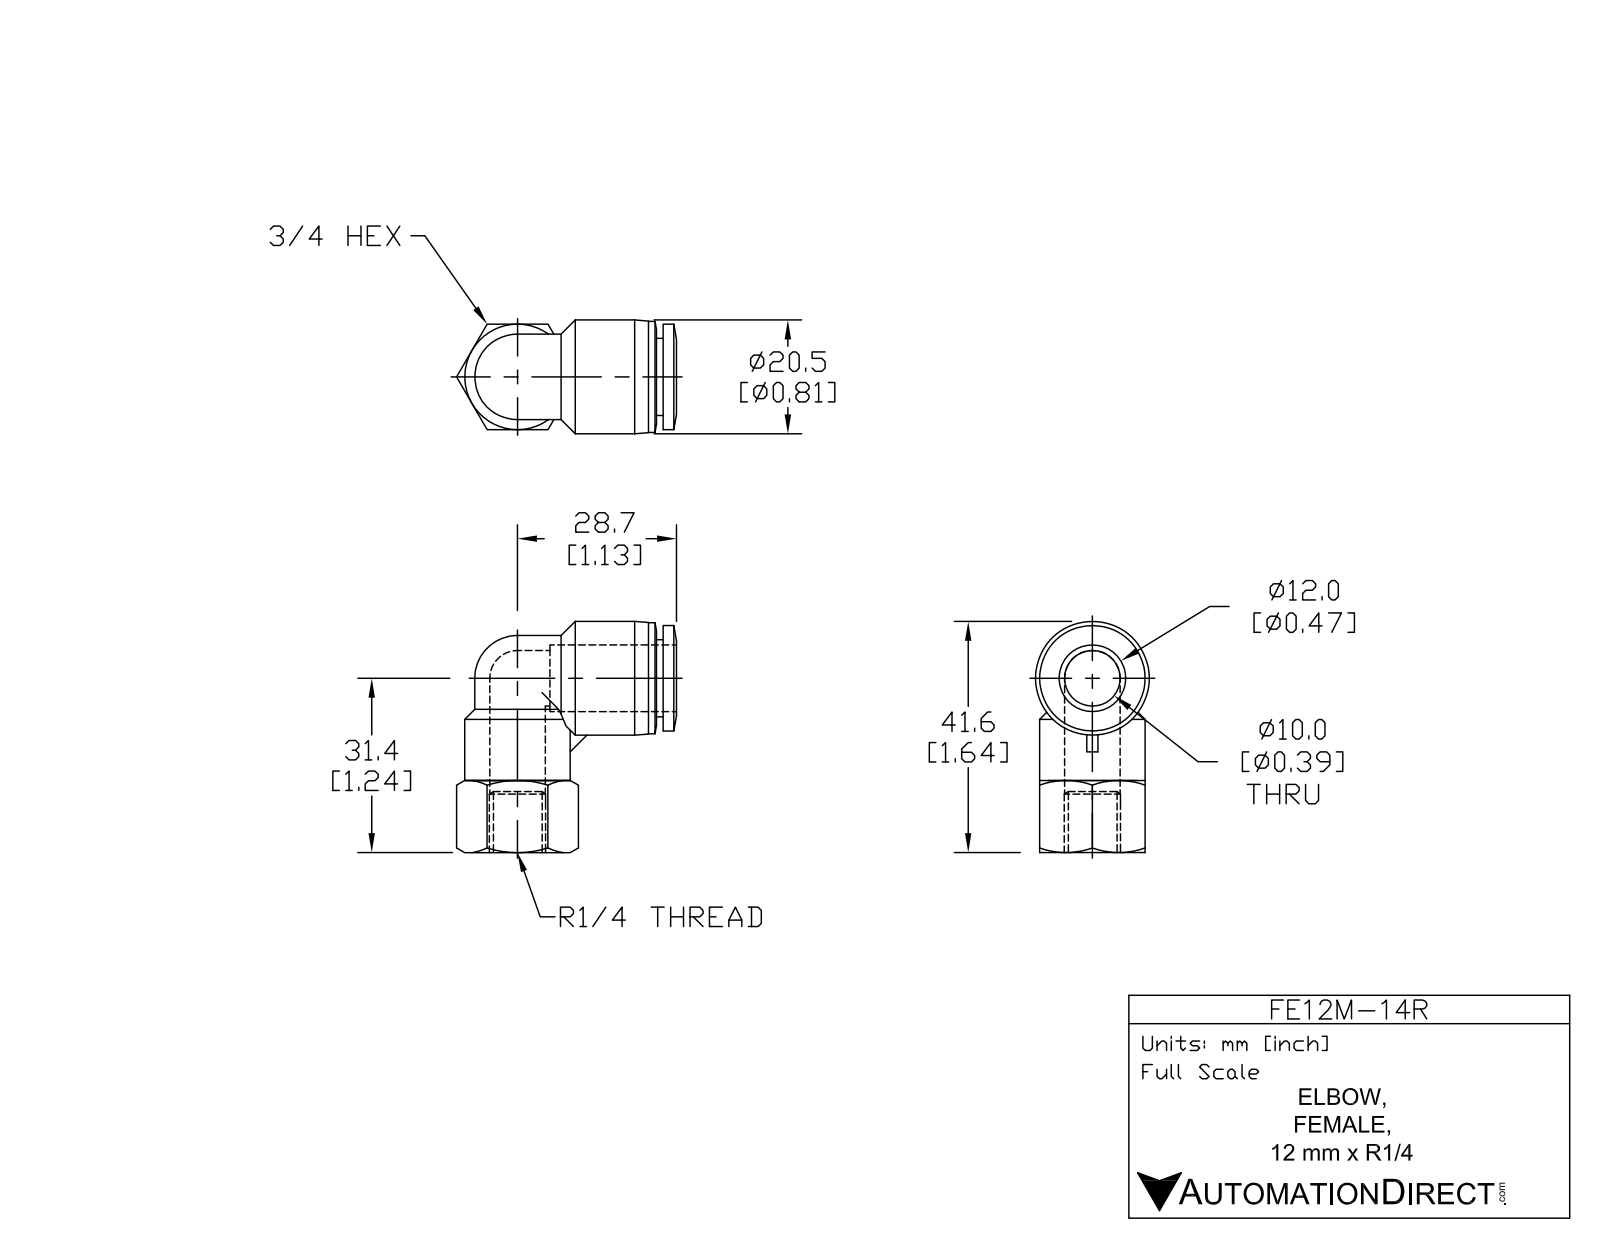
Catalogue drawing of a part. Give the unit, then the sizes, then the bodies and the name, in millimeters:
Units: millimetres
Overall size (bounding box): 41.7 × 39.6 × 20.5
Round holes (diameter × count): ⌀10 ×2, ⌀12.3 ×1
Round bosses / shafts (diameter × count): ⌀19 ×2, ⌀20.5 ×1, ⌀20 ×1, ⌀15.4 ×1, ⌀13.9 ×1
Partial cylindrical surfaces — rounded edges, fillets, slot ends (radius × count): R7.7 ×1
Main face-to-face distances: 19, 1.2, 11, 19.3, 20.5, 22.9, 3.6, 2.4, 8.5, 10.5
Volume: 10 100 mm³ · Surface area: 6 356 mm²
Bodies: 1 solid, 66 faces (16 planar, 19 cylindrical, 31 other)
Part name (STEP PRODUCT): FE12M-14R
STEP written by: SolidWorks 2015 (AUTOMOTIVE_DESIGN)
